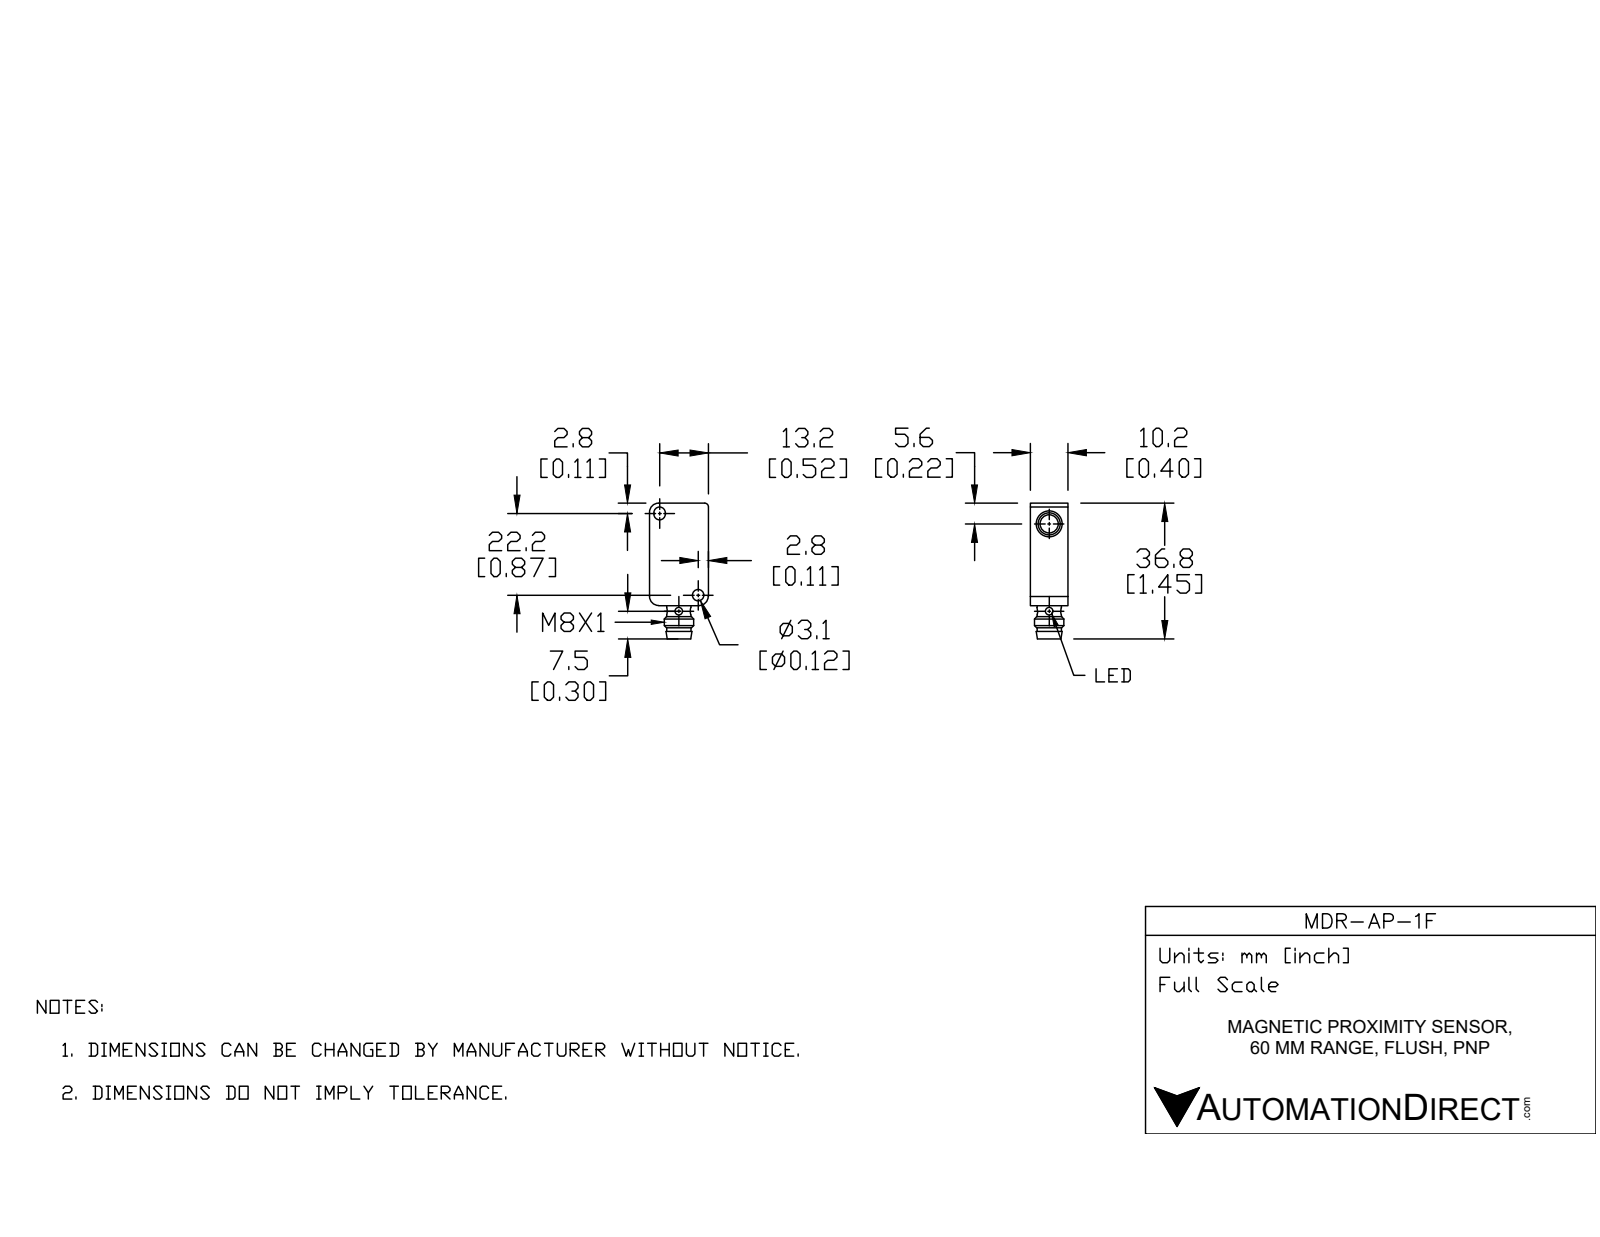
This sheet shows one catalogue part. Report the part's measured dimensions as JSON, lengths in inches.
{"part_name": "MDR-AP-1F", "step_written_by": "SolidWorks 2017 (AUTOMOTIVE_DESIGN)", "units": "inches", "bodies": {"solids": 1, "faces": 57, "planar": 16, "cylindrical": 35, "other": 6}, "overall_size": [1.449, 0.63, 0.402], "volume_in3": 0.277, "surface_area_in2": 3.489, "round_holes": [[0.079, 2], [0.122, 1], [0.197, 1], [0.22, 1], [0.276, 1]], "round_bosses_or_shafts": [[0.315, 1], [0.26, 1], [0.236, 1]], "partial_cylinders_radius": [[0.098, 3], [0.061, 2], [0.039, 1], [0.12, 1]], "face_to_face_distances": [0.402, 0.63, 1.094, 0.61, 0.02, 0.157, 1.252, 0.118, 0.197, 0.354], "hole_center_spacings": [0.267, 0.933]}
